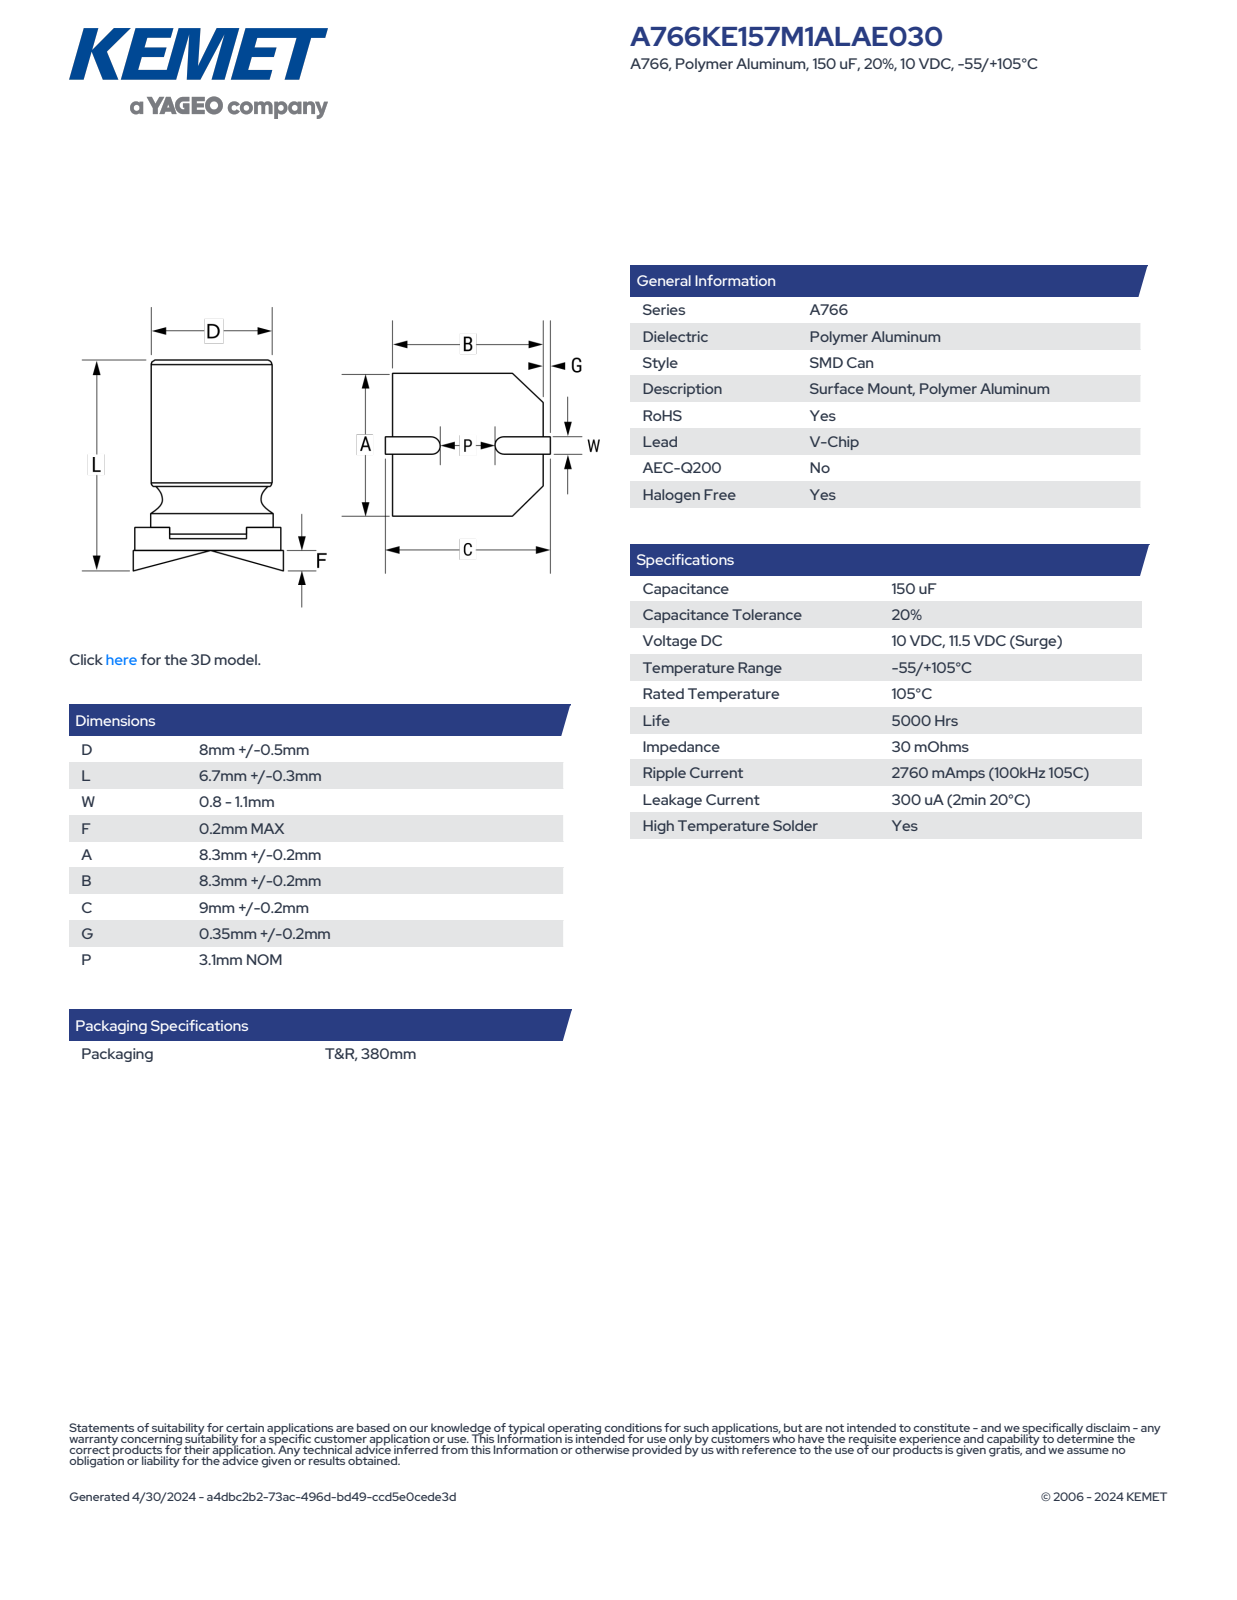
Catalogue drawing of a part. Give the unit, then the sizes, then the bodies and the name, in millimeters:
Units: millimetres
Overall size (bounding box): 9.2 × 8.5 × 7
Round bosses / shafts (diameter × count): ⌀8.13 ×1
Partial cylindrical surfaces — rounded edges, fillets, slot ends (radius × count): R0.2 ×2, R3.38 ×1, R4.25 ×1
Main face-to-face distances: 0.35, 6.8, 6.45, 8.5, 1.75, 1.4, 5.05, 0.55, 1.95, 7
Volume: 369 mm³ · Surface area: 470 mm²
Bodies: 5 solids, 76 faces (59 planar, 11 cylindrical, 6 other)
Part name (STEP PRODUCT): CAC_KS_8X6.7_D8.5L7W1.1F0.2A8.5B8.5C9.2P3.1
STEP written by: SolidWorks 2014 (AUTOMOTIVE_DESIGN)
